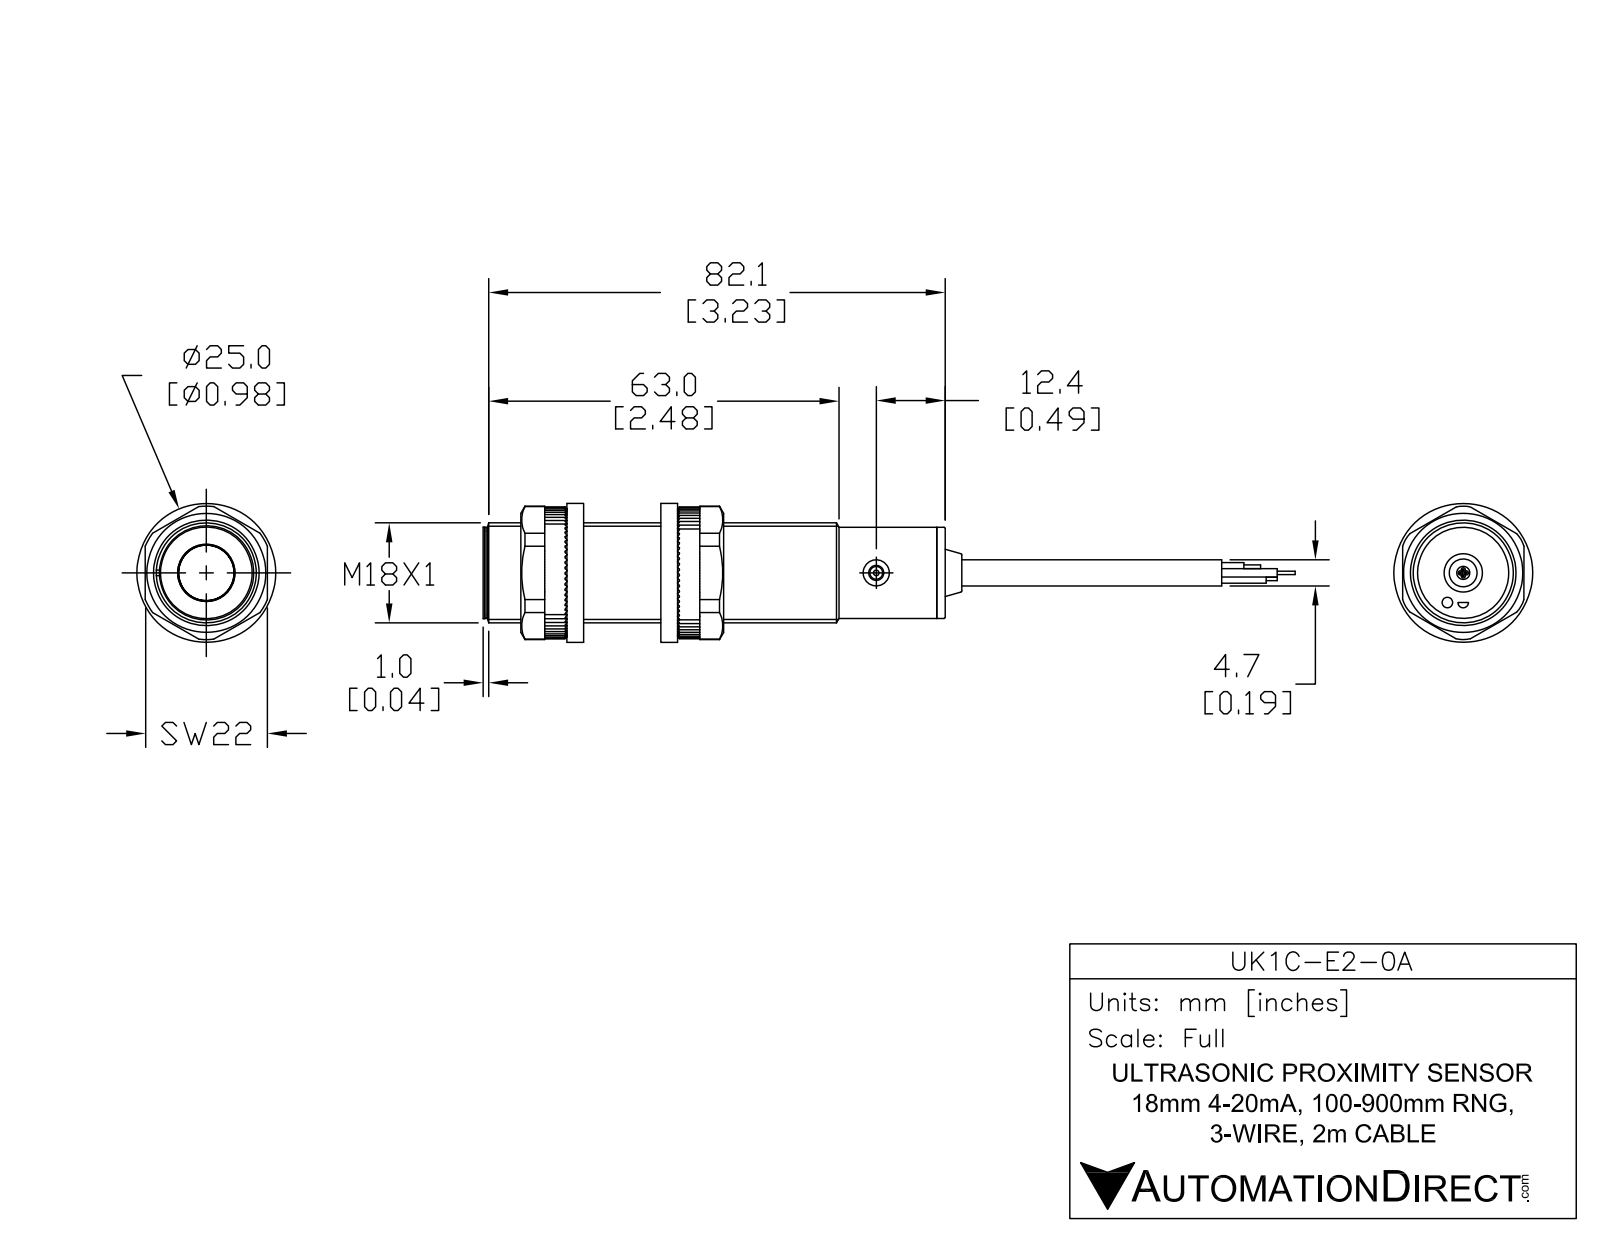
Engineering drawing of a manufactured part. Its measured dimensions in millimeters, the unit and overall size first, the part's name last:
Units: millimetres
Overall size (bounding box): 122.7 × 18 × 18
Round holes (diameter × count): ⌀4.7 ×2, ⌀2.7 ×1
Round bosses / shafts (diameter × count): ⌀18 ×1, ⌀16.4 ×1, ⌀15.8 ×1, ⌀9.5 ×1, ⌀4.8 ×1, ⌀2.3 ×1
Main face-to-face distances: 81.1, 82.6, 1.5, 1, 82.1, 83.6, 1, 82.1, 83.6, 82.7
Volume: 21 060 mm³ · Surface area: 6 897 mm²
Bodies: 6 solids, 55 faces (17 planar, 24 cylindrical, 14 other)
Part name (STEP PRODUCT): UK1C-E2-0A
STEP written by: SolidWorks 2017 (AUTOMOTIVE_DESIGN)
